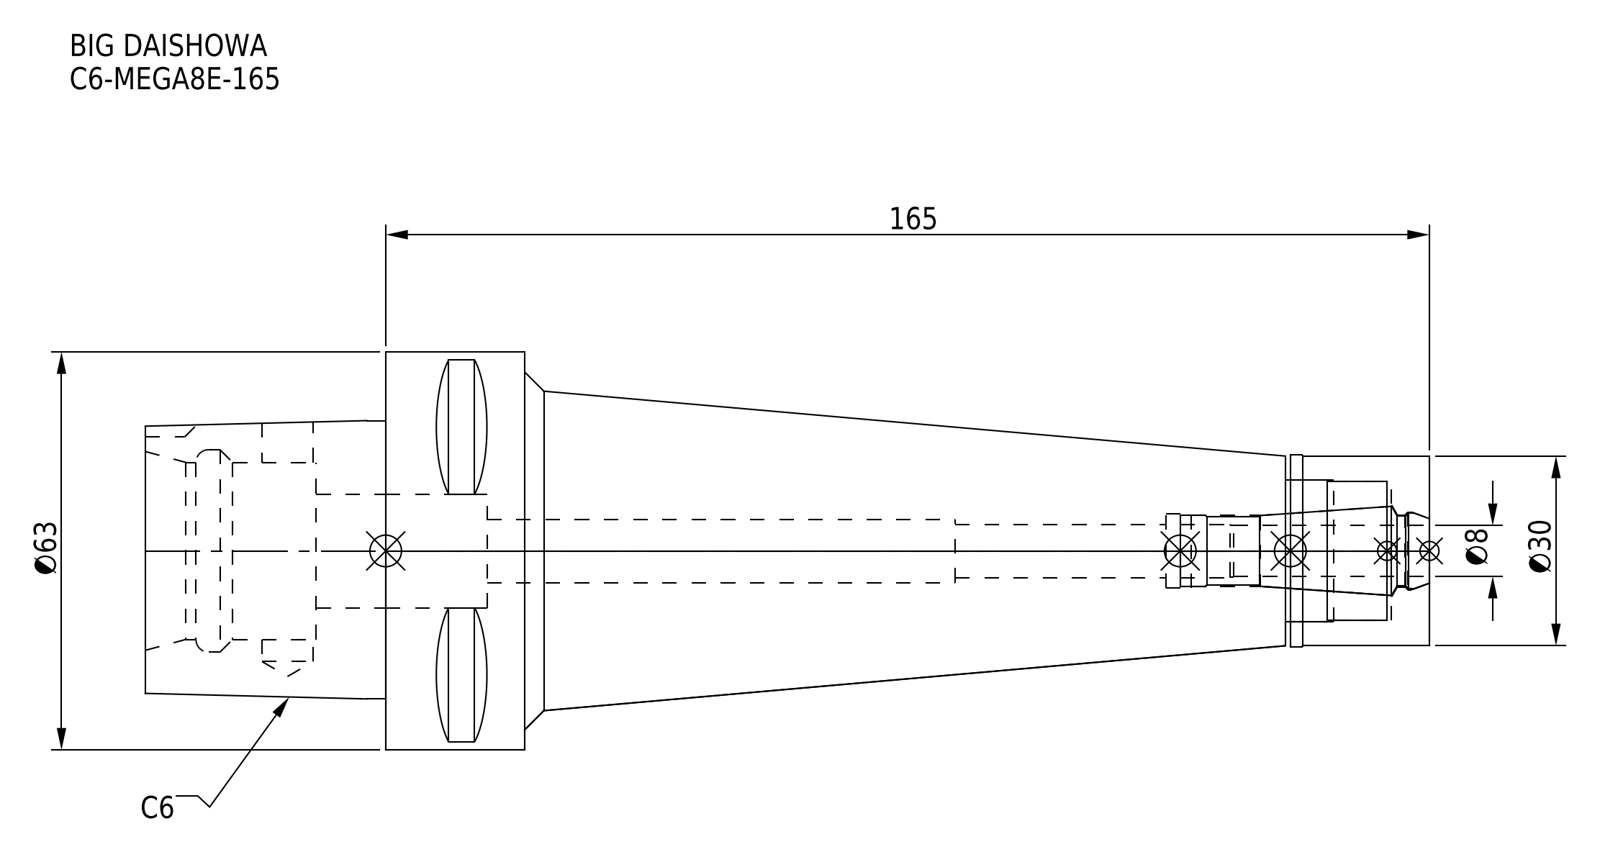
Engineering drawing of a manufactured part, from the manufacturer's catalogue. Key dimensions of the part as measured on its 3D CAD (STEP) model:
Part name (STEP PRODUCT): MEN8_1.stp; DXF_TEMP_ASSY_ASM_4_ASM.stp; C6-MEGA8E-165-080_ASM.stp; C6-MEGA8E-165-080.stp (+3 more)
STEP written by: SolidWorks 2019 (CONFIG_CONTROL_DESIGN)
Units: millimetres
Bodies: 2 solids, 100 faces (37 planar, 39 cylindrical, 24 other)
Overall size (bounding box): 203 × 63 × 63
Volume: 259 000 mm³ · Surface area: 44 091 mm²
Round holes (diameter × count): ⌀8.1 ×1, ⌀8.4 ×1, ⌀10 ×1, ⌀11.2 ×1, ⌀11.4 ×1, ⌀11.8 ×1, ⌀12.3 ×1, ⌀18 ×1, ⌀22 ×1, ⌀22.5 ×1, ⌀28 ×1, ⌀32 ×1
Round bosses / shafts (diameter × count): ⌀63 ×1, ⌀30.3 ×1, ⌀30 ×1
Partial cylindrical surfaces — rounded edges, fillets, slot ends (radius × count): R5 ×1
Main face-to-face distances: 143, 22, 165, 27, 203, 60, 38, 6, 16, 176
